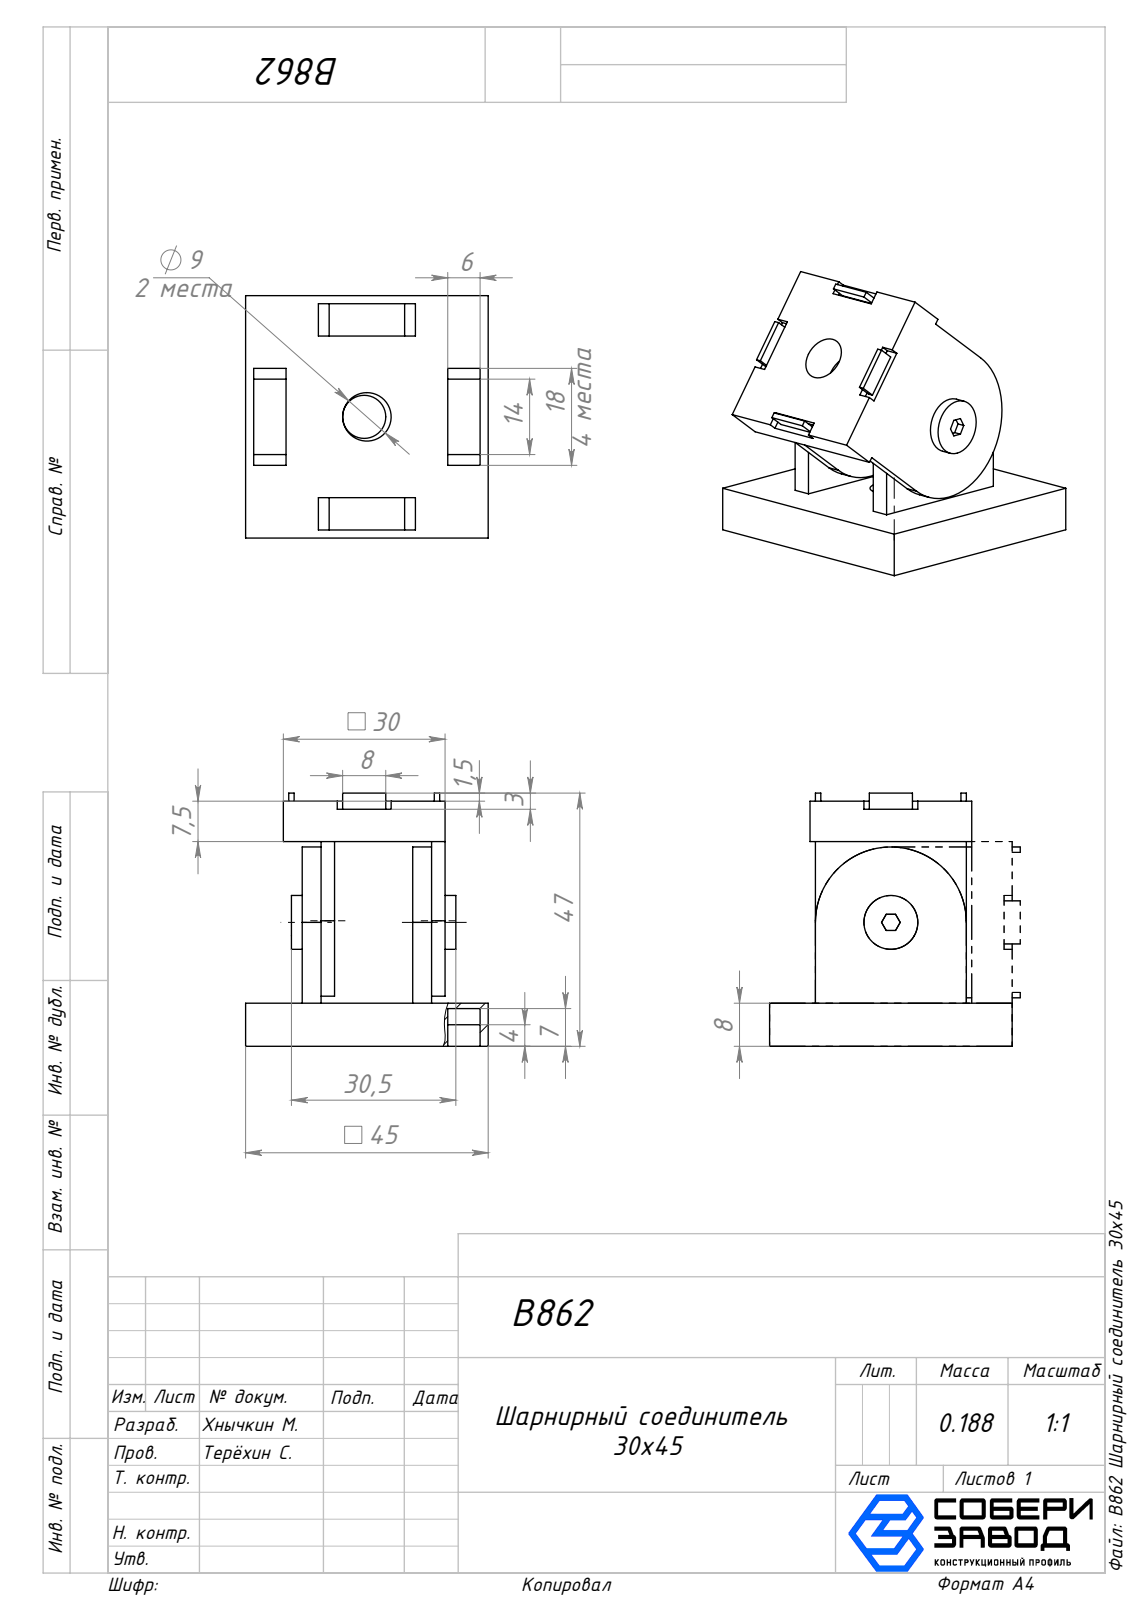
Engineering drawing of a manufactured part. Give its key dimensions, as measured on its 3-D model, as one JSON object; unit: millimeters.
{"part_name": "Соединитель_00; B862 Шарнирный соединитель 30х45; Винт_00; Квадратная опора_00", "step_written_by": "SolidWorks 2025 (AUTOMOTIVE_DESIGN)", "units": "millimeters", "bodies": {"solids": 4, "faces": 143, "planar": 119, "cylindrical": 24, "other": 0}, "overall_size": [50.11, 48.58, 45], "volume_mm3": 28243, "surface_area_mm2": 16831, "round_holes": [[3, 1], [8, 1], [9, 1]], "round_bosses_or_shafts": [[10, 1]], "partial_cylinders_radius": [[14, 2]], "face_to_face_distances": [20.5, 8, 6, 3.5, 2.5, 24, 7, 23, 14, 1.5]}
